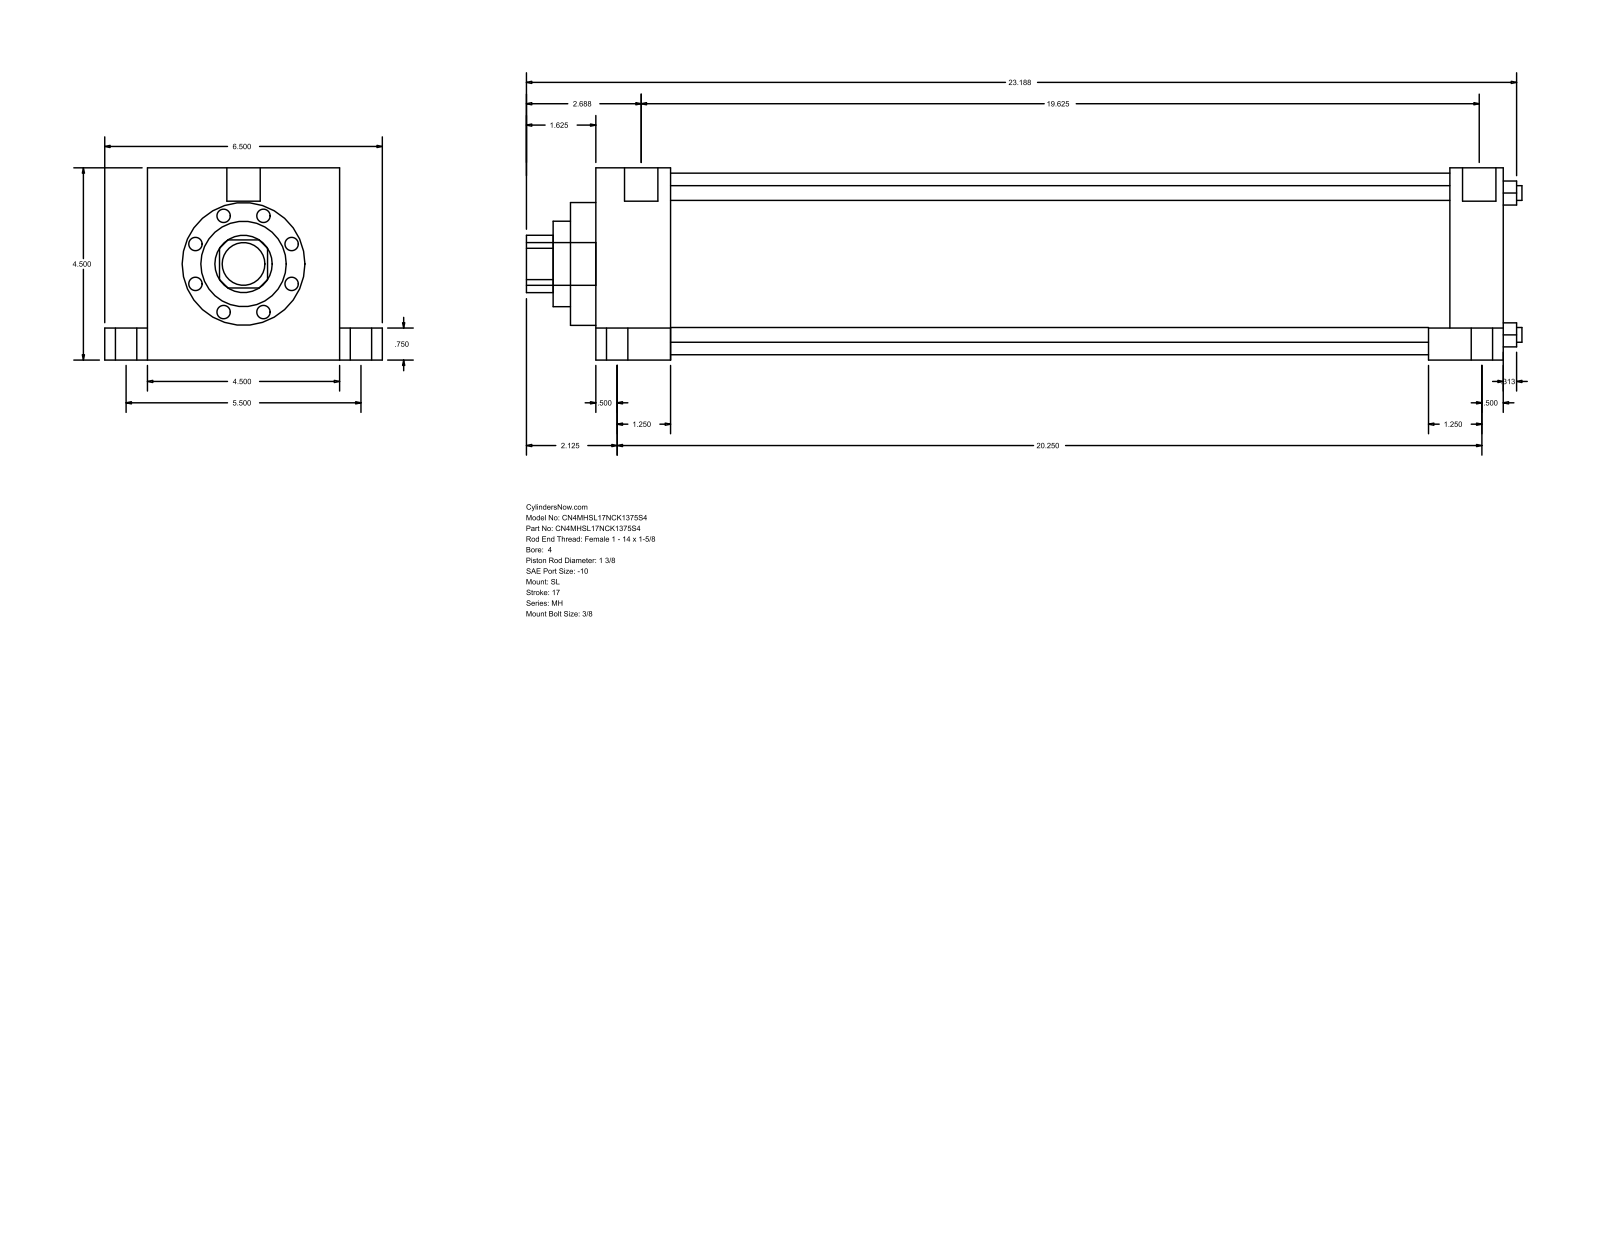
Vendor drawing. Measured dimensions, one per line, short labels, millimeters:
name: MH_SL__0400_1.375
written by: GSSL Pune (CONFIG_CONTROL_DESIGN)
unit: mm
bodies: 0 solids, 110 faces (77 planar, 33 cylindrical, 0 other)
size: 592.14 × 165.1 × 114.3
holes: 4× ⌀8.76, 1× ⌀34.92, 1× ⌀50.8, 1× ⌀73.03, 1× ⌀107.95
bosses: 4× ⌀19.05, 4× ⌀12.7, 4× ⌀8.73, 2× ⌀19.84, 1× ⌀25.4
rounds: 1× R17.06
face distances: 114.3, 539.75, 44.45, 495.3, 508, 463.55, 31.75, 25.4, 139.7, 19.05
hole spacings: 59.62, 84.32, 119.25
